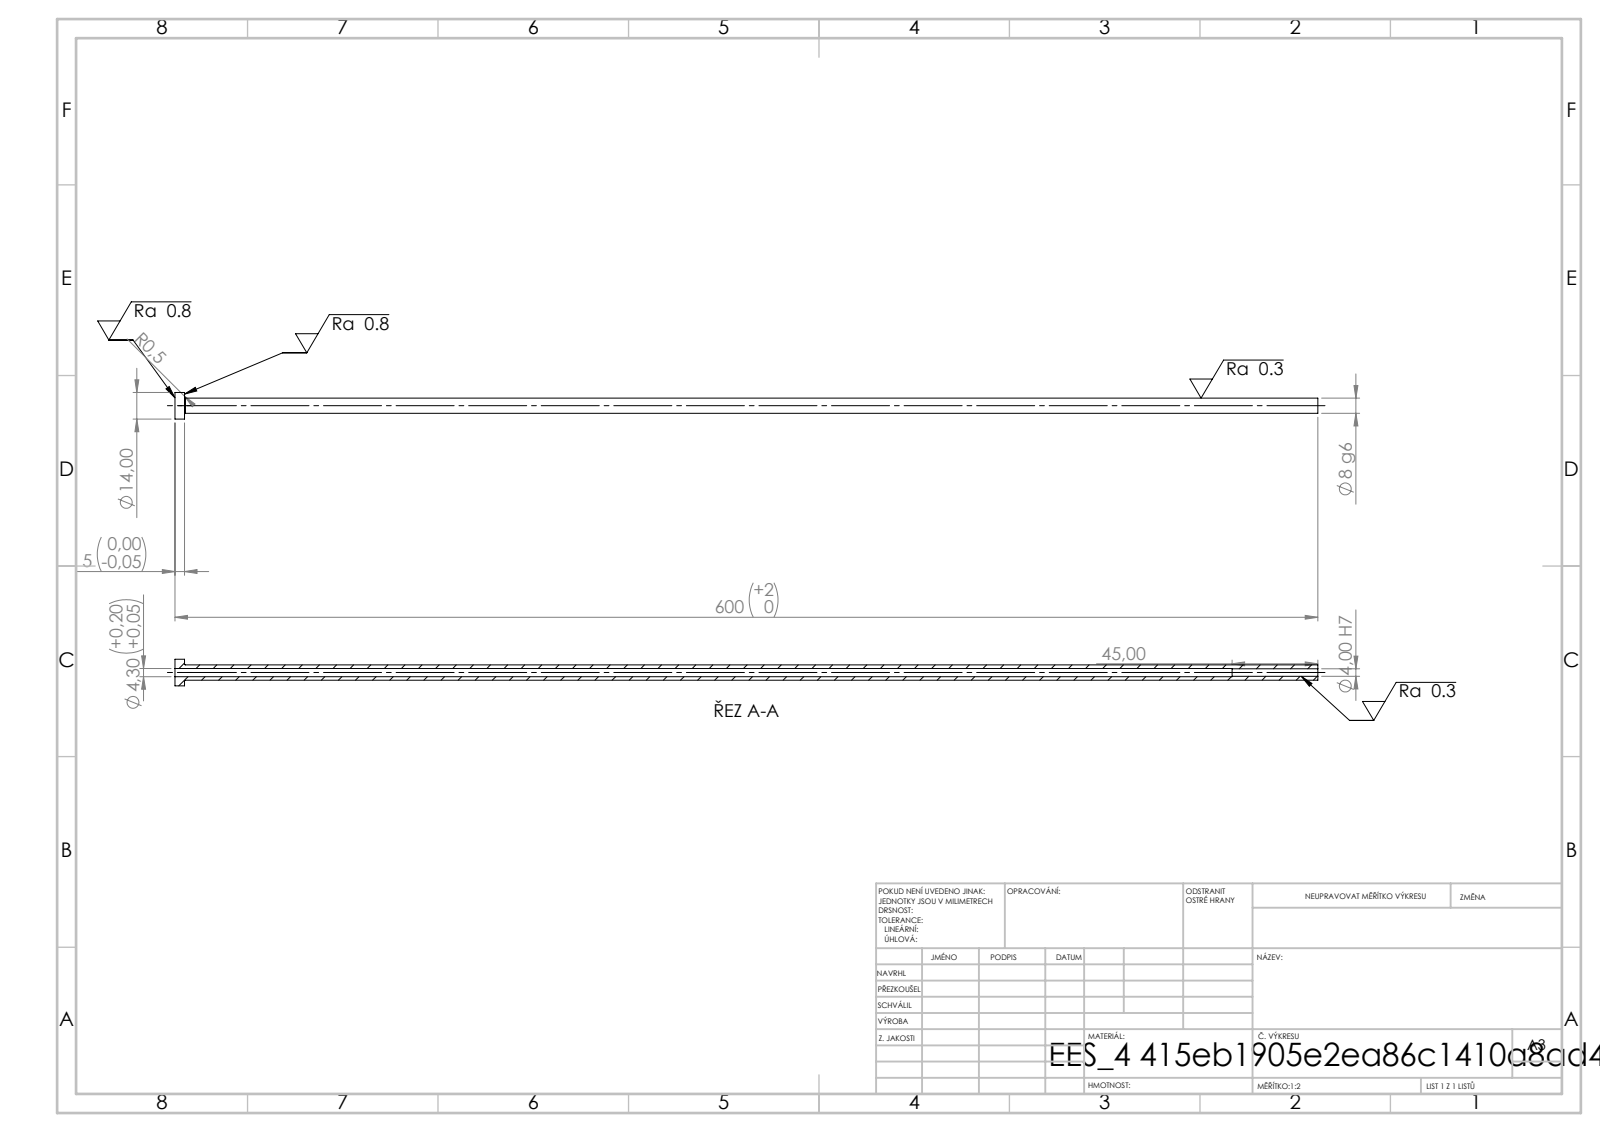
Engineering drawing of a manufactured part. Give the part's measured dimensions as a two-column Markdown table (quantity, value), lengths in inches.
| quantity | value |
| --- | --- |
| STEP written by | SolidWorks 2019 (CONFIG_CONTROL_DESIGN) |
| units | inches |
| bodies | 1 solid, 14 faces (4 planar, 8 cylindrical, 2 other) |
| overall size | 23.622 × 0.551 × 0.551 |
| volume | 1.346 in³ |
| surface area | 36.45 in² |
| round holes (diameter × count) | 0.157 × 1, 0.169 × 1 |
| round bosses / shafts (diameter × count) | 0.551 × 1, 0.315 × 1 |
| main face-to-face distances | 0.197, 23.622, 23.425, 21.85, 21.654, 1.772 |
